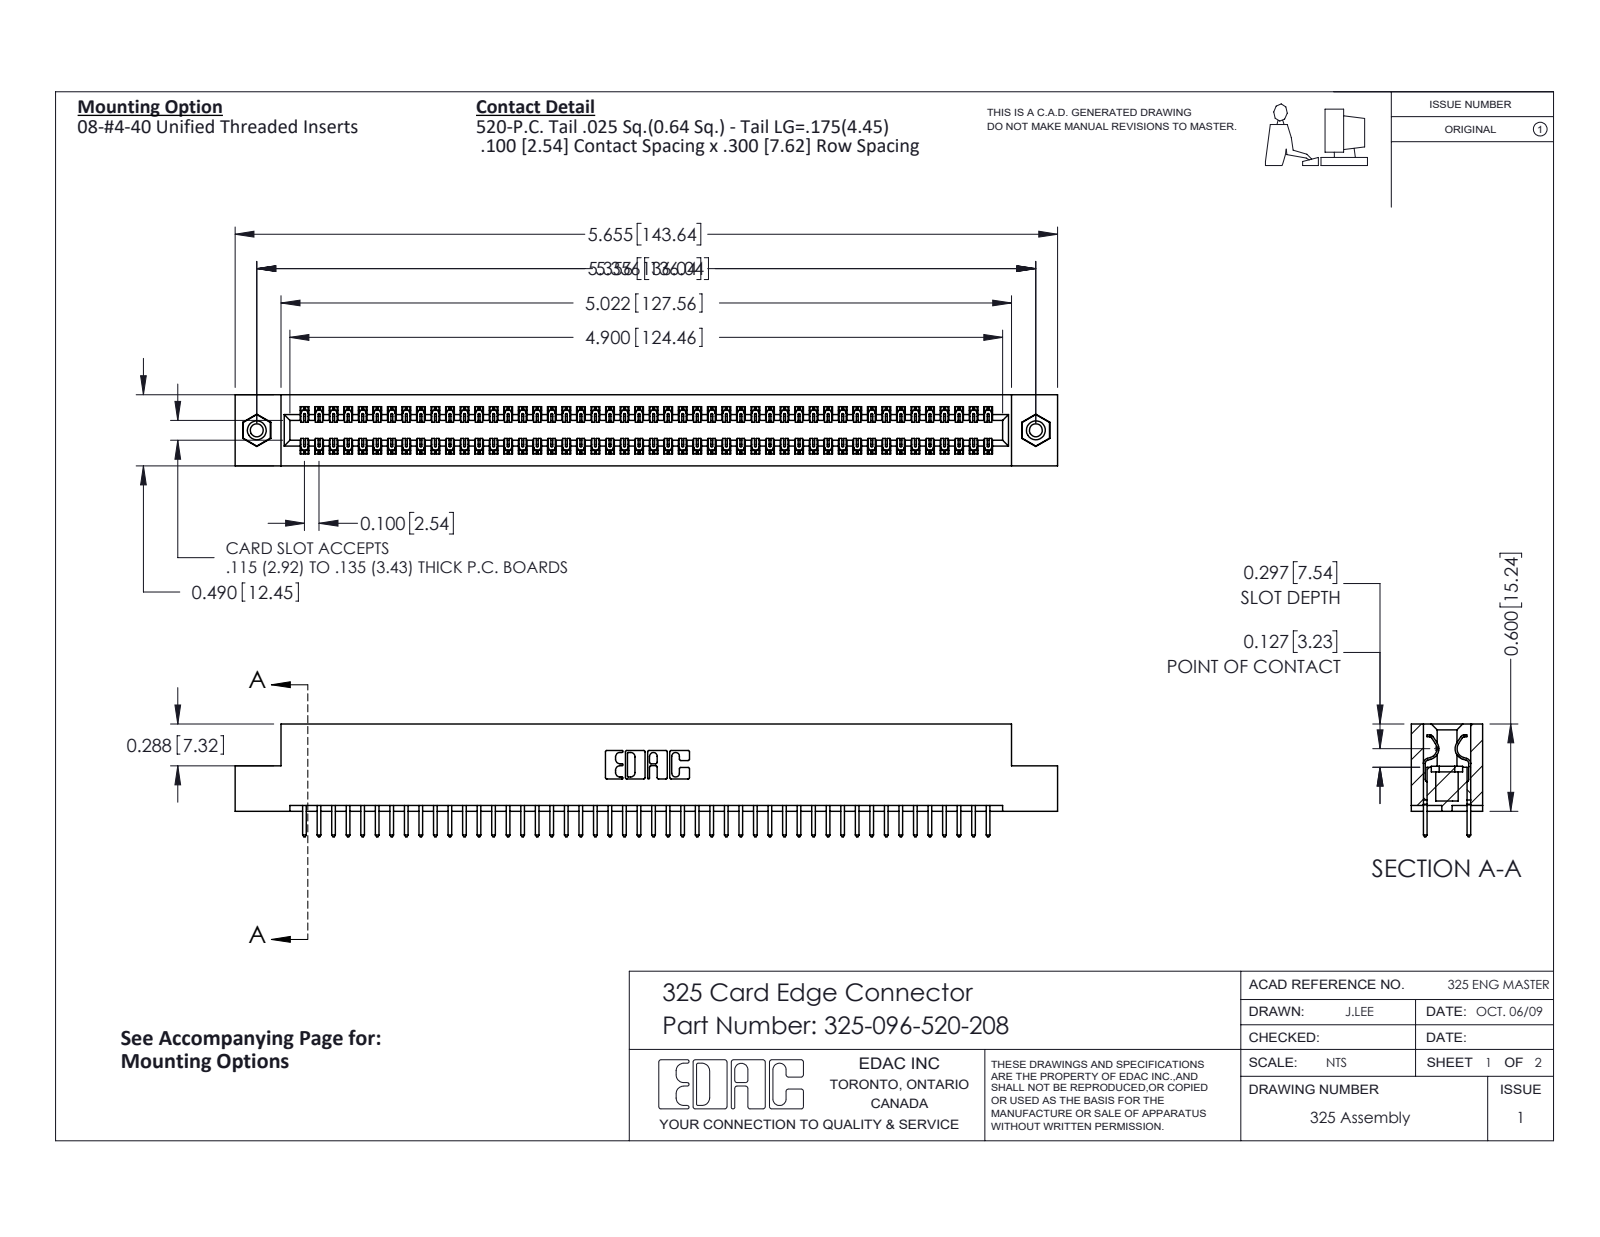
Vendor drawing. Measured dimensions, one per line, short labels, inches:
name: 325-096-520-208; 325 Part_TI; 325-292-001_325-293-120; 345-250-001_345-250-003-102
written by: SolidWorks 2016 (CONFIG_CONTROL_DESIGN)
unit: in
bodies: 99 solids, 5166 faces (3558 planar, 1592 cylindrical, 16 other)
size: 5.655 × 0.775 × 0.49
volume: 1.134 in³; area: 34.79 in²
holes: 2× ⌀0.089, 2× ⌀0.125, 2× ⌀0.16
bosses: 2× ⌀0.155
rounds: 144× R0.006, 96× R0.01, 22× R0.01, 6× R0.007, 6× R0.031, 3× R0.026, 2× R0.014, 2× R0.022
face distances: 0.083, 0.407, 0.3, 0.49, 0.107, 0.383, 0.025, 0.325, 0.275, 0.56
hole spacings: 5.356
